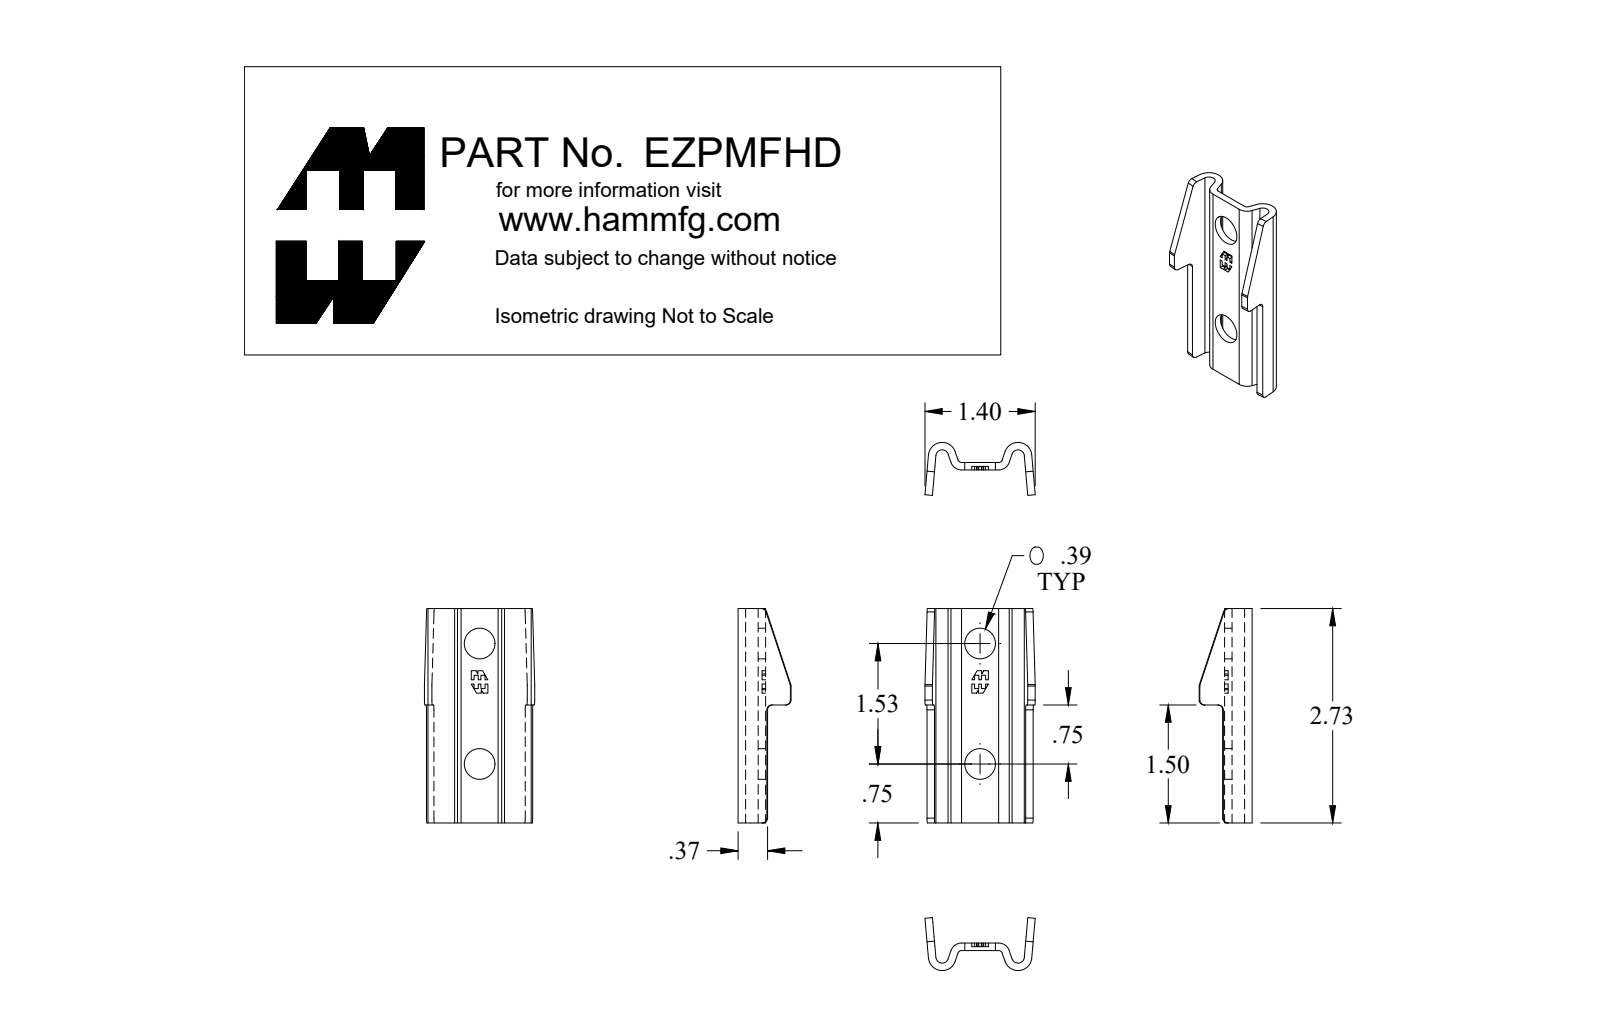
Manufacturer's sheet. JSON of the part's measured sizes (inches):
{"part_name": "EZPMFHD", "step_written_by": "SolidWorks 2018 (AUTOMOTIVE_DESIGN)", "units": "inches", "bodies": {"solids": 1, "faces": 74, "planar": 52, "cylindrical": 22, "other": 0}, "overall_size": [2.726, 1.402, 0.673], "volume_in3": 0.543, "surface_area_in2": 12.73, "round_holes": [[0.39, 2]], "partial_cylinders_radius": [[0.062, 9], [0.048, 2], [0.08, 2], [0.143, 2], [0.175, 2], [0.063, 1]], "face_to_face_distances": [0.095, 0.095, 2.726, 0.299, 1.5, 1.226, 0.05, 0.045, 0.054, 0.058], "hole_center_spacings": [1.531]}
